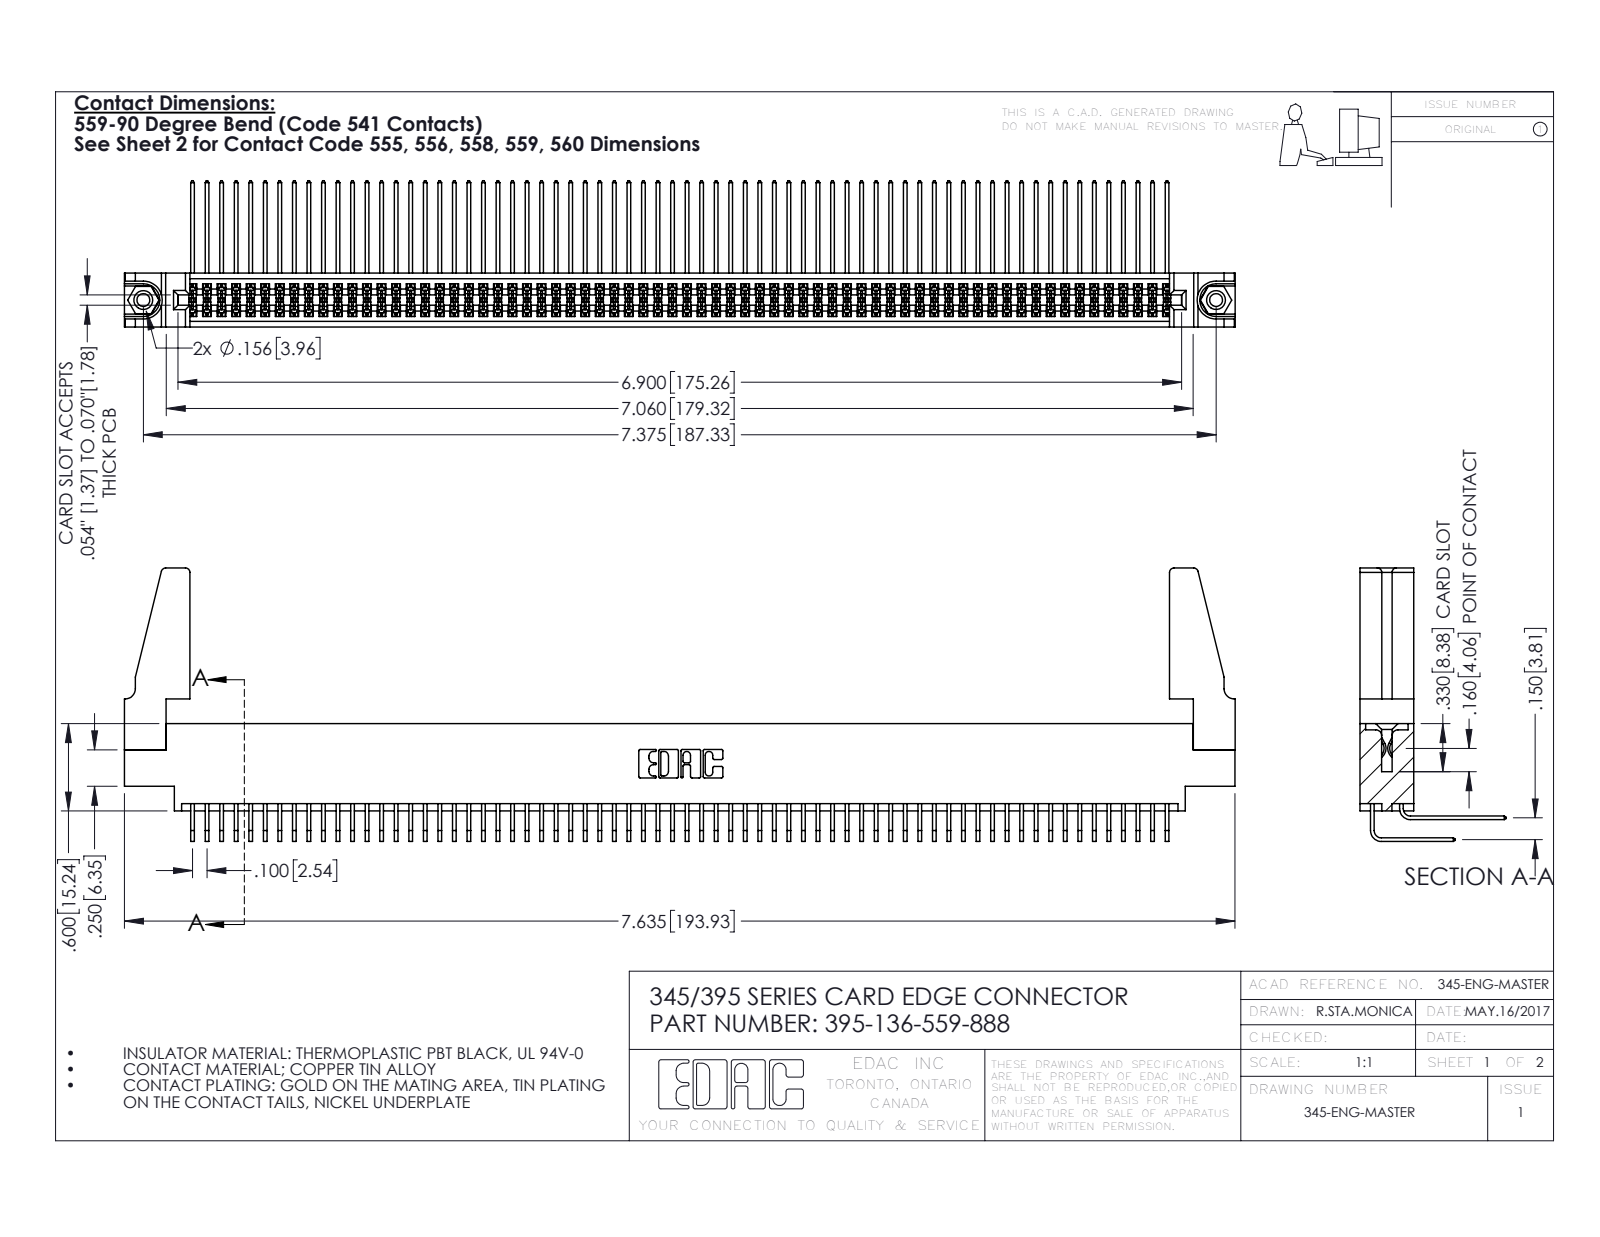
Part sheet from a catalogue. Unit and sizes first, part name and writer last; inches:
Units: inches
Overall size (bounding box): 7.636 × 1.879 × 1.005
Round holes (diameter × count): ⌀0.089 ×2, ⌀0.125 ×2, ⌀0.156 ×2, ⌀0.064 ×1
Round bosses / shafts (diameter × count): ⌀0.155 ×2
Partial cylindrical surfaces — rounded edges, fillets, slot ends (radius × count): R0.006 ×272, R0.01 ×22, R0.03 ×8, R0.007 ×6, R0.031 ×6, R0.026 ×3, R0.014 ×2, R0.019 ×2
Main face-to-face distances: 0.072, 0.298, 0.37, 0.098, 0.272, 0.025, 0.2, 0.225, 0.175, 0.15
Hole centre spacings: 0.27, 7.139, 7.375
Volume: 1.404 in³ · Surface area: 56.82 in²
Bodies: 141 solids, 7326 faces (4916 planar, 2394 cylindrical, 16 other)
Part name (STEP PRODUCT): 345-292-001_559 Tail - 2; 345-250-001_345-250-001-102; 395-136-559-888; 345-220-078_345-220-088 (+2 more)
STEP written by: SolidWorks 2016 (CONFIG_CONTROL_DESIGN)
